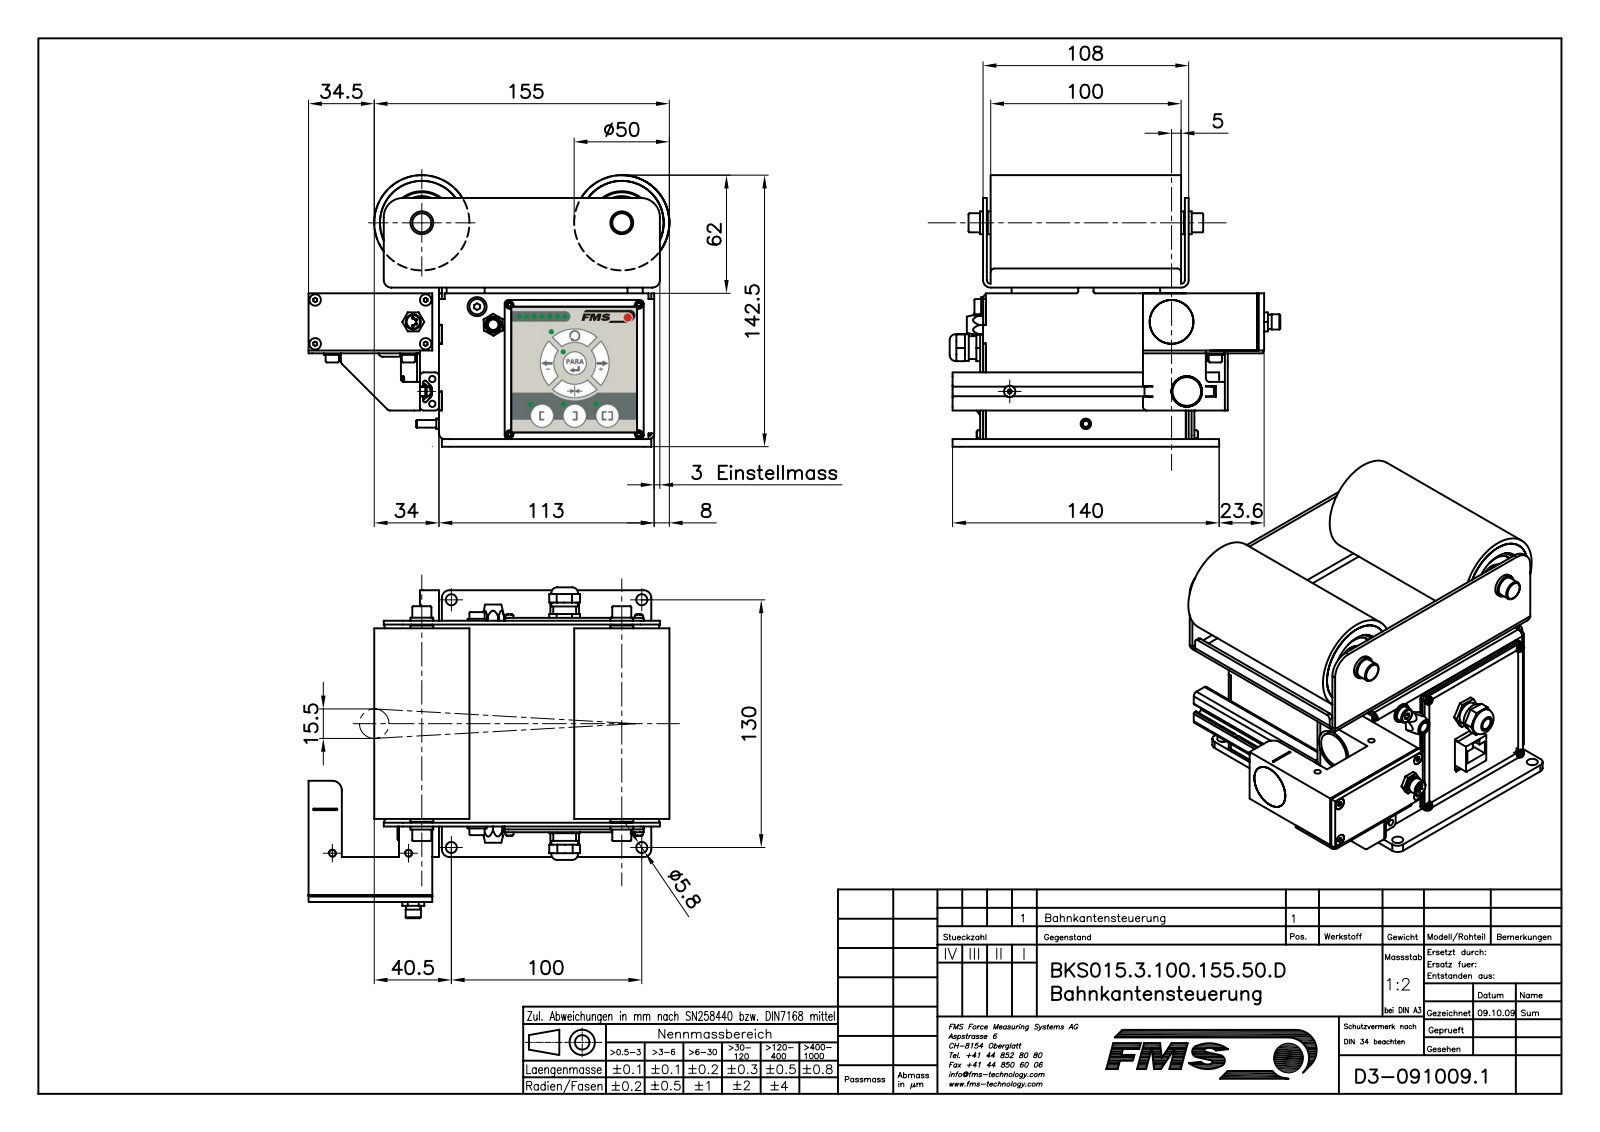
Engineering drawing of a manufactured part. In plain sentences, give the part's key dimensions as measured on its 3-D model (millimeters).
The part is named "K0910091; K0910092; K0910095; K0901207 (+8 more)". Its 3-D file was written by "Mechanical Desktop 2007 (CONFIG_CONTROL_DESIGN)". It is 95 solids with 2348 faces: 1117 planar, 975 cylindrical and 256 other. Overall it measures 189.5 by 174.1 by 142.5 millimeters. Its volume is 489 852 cubic millimeters and its surface area 381 028 square millimeters. Round holes: 14 of diameter 3.2, 10 of diameter 4.5, 9 of diameter 6, 8 of diameter 2.5, 7 of diameter 2.14, 6 of diameter 2.6, 5 of diameter 4.3, 4 of diameter 1.9, 4 of diameter 3.42, 4 of diameter 5.4, 4 of diameter 5.8, 3 of diameter 4.2. Round bosses or shafts: 13 of diameter 4, 11 of diameter 8, 6 of diameter 3, 5 of diameter 9, 4 of diameter 10, 4 of diameter 9.4, 4 of diameter 7, 4 of diameter 4.2. Partial cylindrical surfaces (rounded edges, fillets, slot ends): 48 of radius 0.25, 27 of radius 2, 19 of radius 3, 12 of radius 1.5, 10 of radius 5, 9 of radius 8, 8 of radius 1, 8 of radius 4. The main face-to-face distances are 2, 1.5, 4, 108, 106, 111.5, 81.5, 83.5, 0.5, 85.5. The hole center spacings are 66.18, 68, 2.62, 11.77, 27.02, 45.47, 48.08, 56.68.
